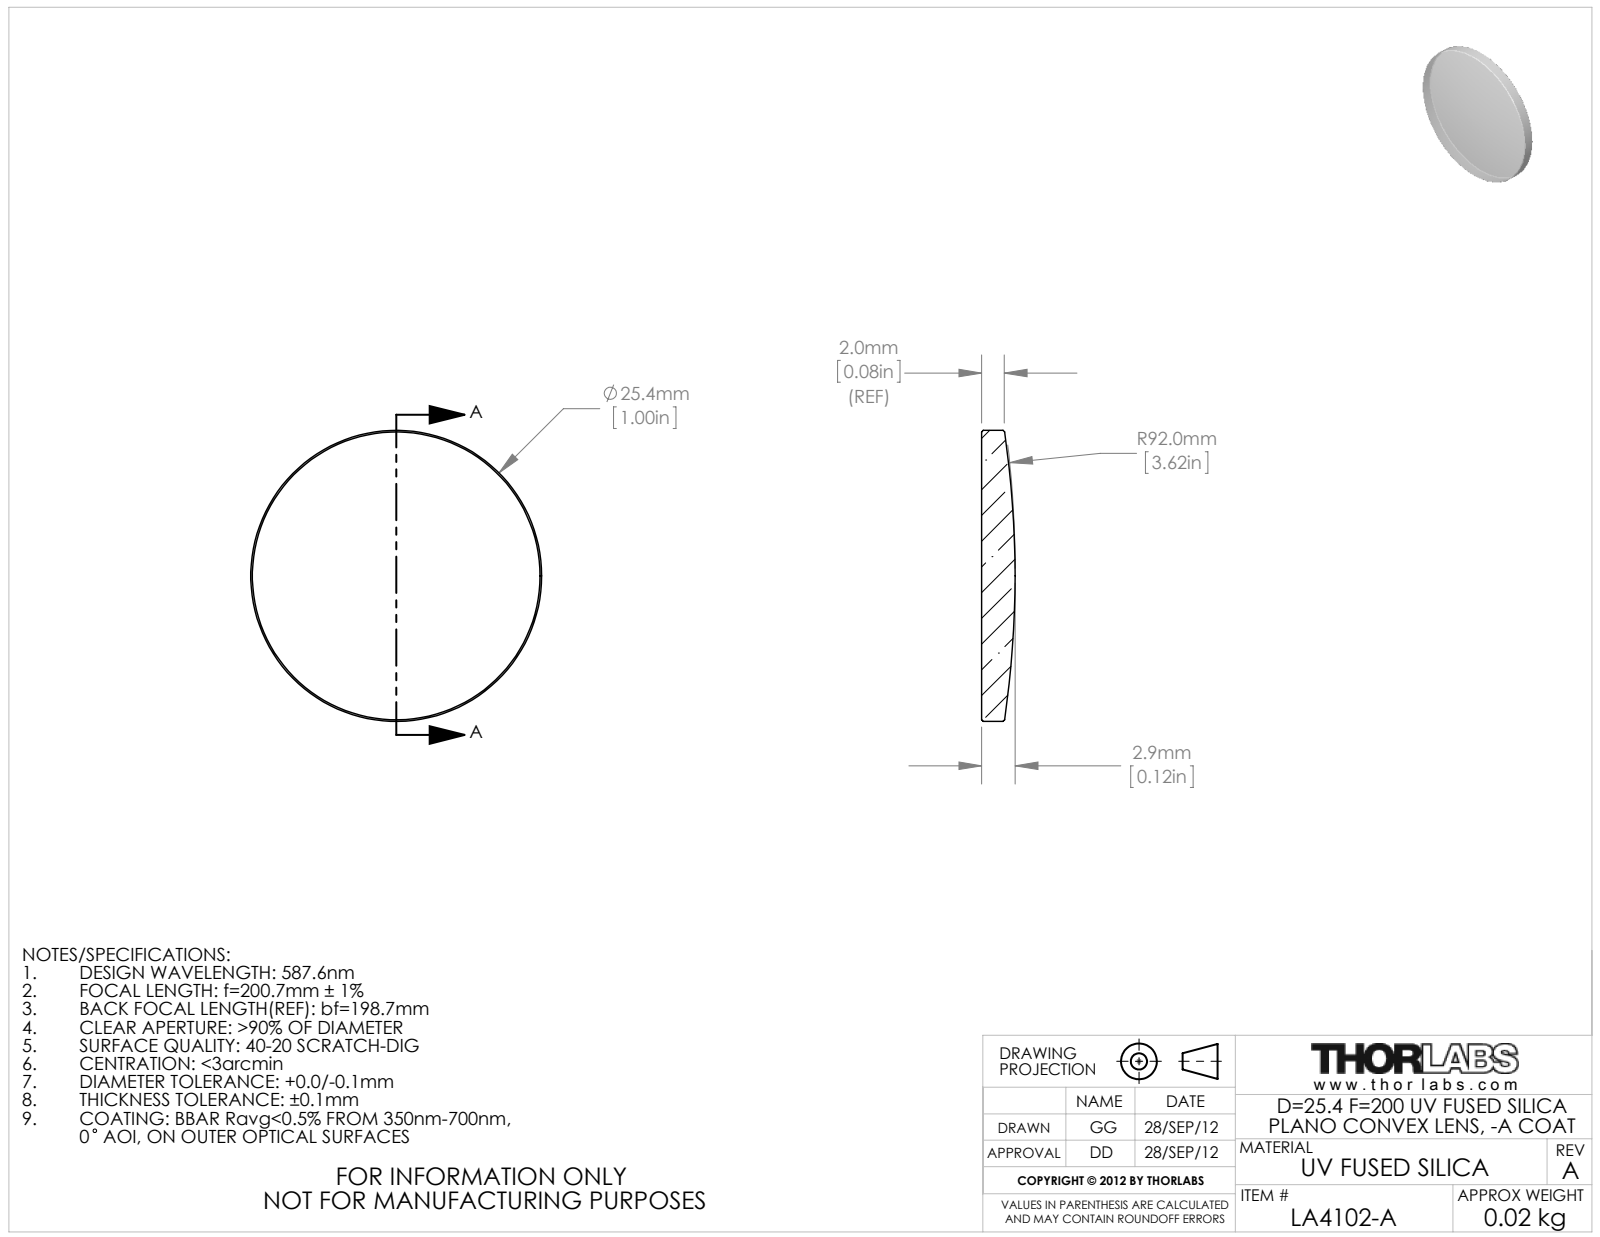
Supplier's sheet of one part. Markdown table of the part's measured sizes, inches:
| quantity | value |
| --- | --- |
| part name | 24987-E0W |
| STEP written by | SolidWorks 2011 (AUTOMOTIVE_DESIGN) |
| units | inches |
| bodies | 1 solid, 9 faces (1 planar, 2 cylindrical, 6 other) |
| overall size | 1 × 1 × 0.115 |
| volume | 0.075 in³ |
| surface area | 1.801 in² |
| round bosses / shafts (diameter × count) | 1 × 1 |
